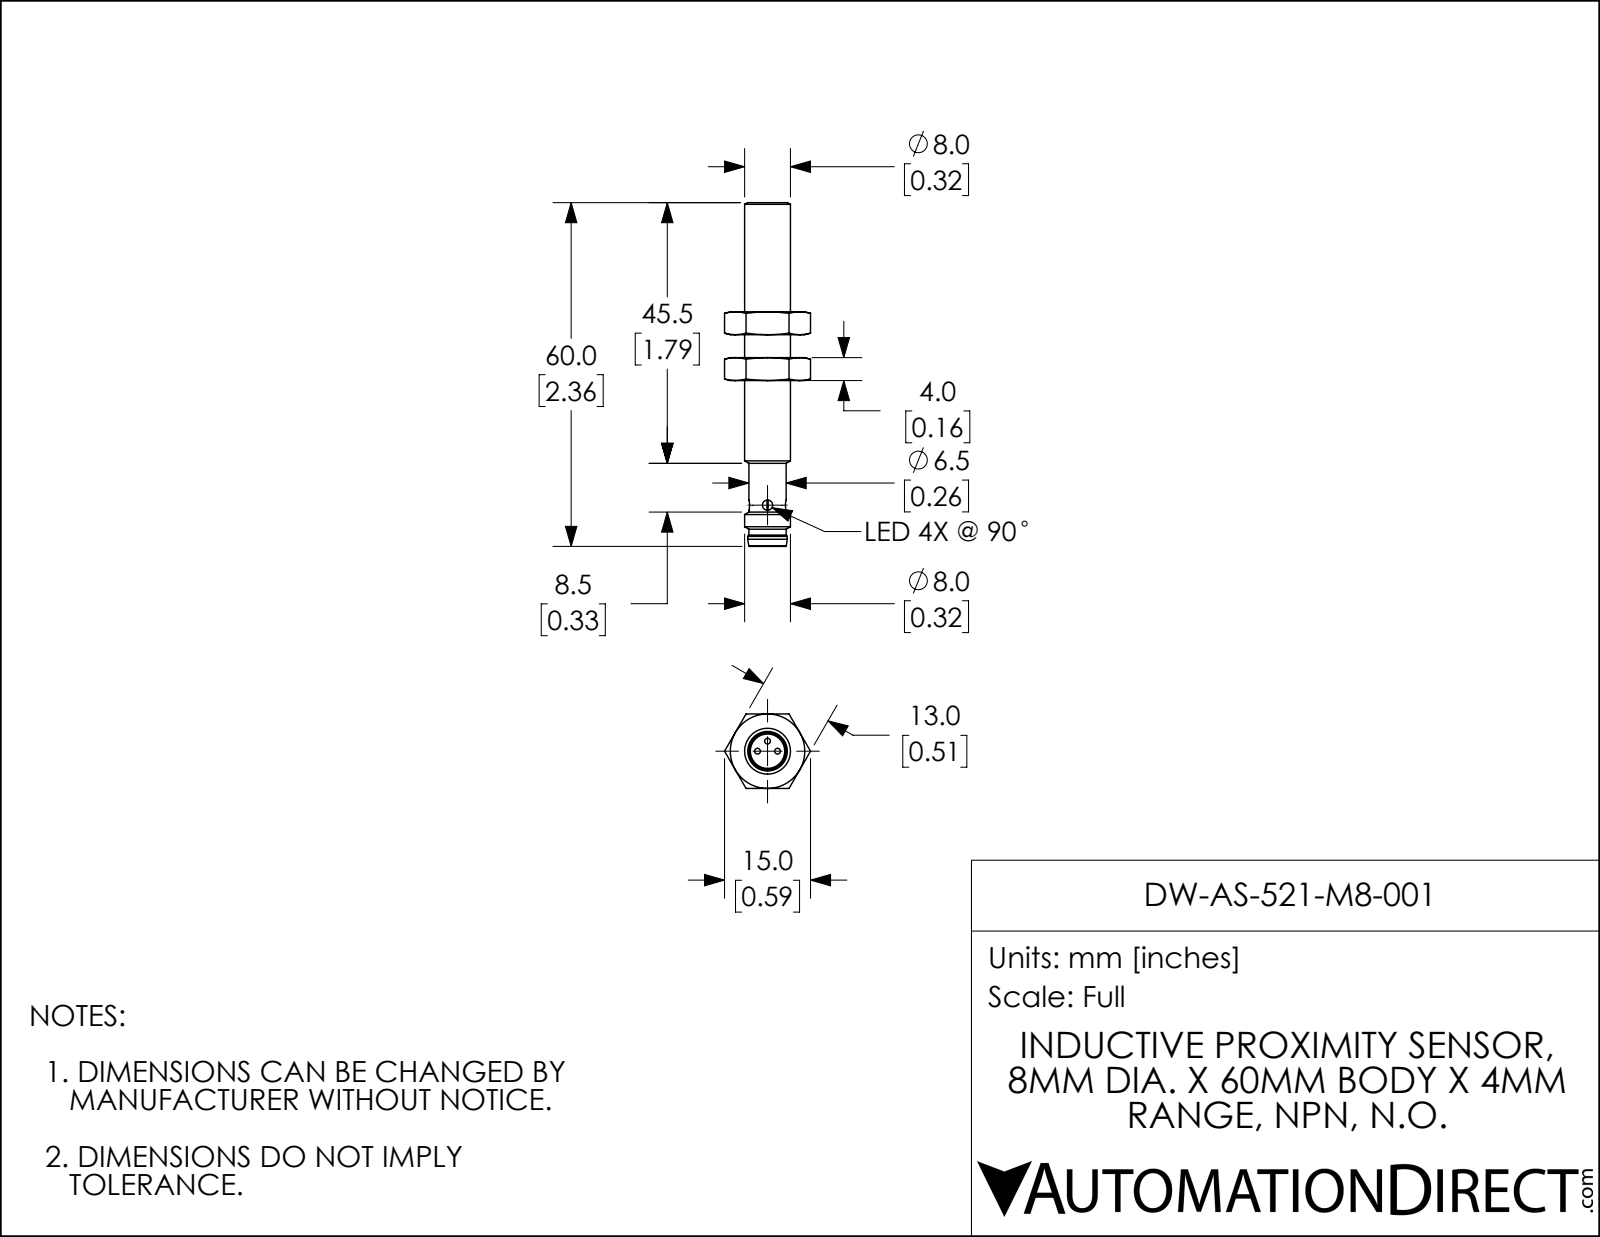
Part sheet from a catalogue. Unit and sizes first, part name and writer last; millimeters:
Units: millimetres
Overall size (bounding box): 60 × 8 × 8
Round holes (diameter × count): ⌀1.8 ×2, ⌀6 ×1
Round bosses / shafts (diameter × count): ⌀1 ×3, ⌀8 ×1, ⌀6.9 ×1, ⌀6.5 ×1
Partial cylindrical surfaces — rounded edges, fillets, slot ends (radius × count): R3.1 ×1
Main face-to-face distances: 55, 5, 60, 4.2, 14.5, 9.5, 45.5, 3, 2, 11.5
Volume: 2 670 mm³ · Surface area: 1 701 mm²
Bodies: 1 solid, 44 faces (13 planar, 21 cylindrical, 10 other)
Part name (STEP PRODUCT): DW-AS-521-M8-001
STEP written by: SolidWorks 2018 (AUTOMOTIVE_DESIGN)
